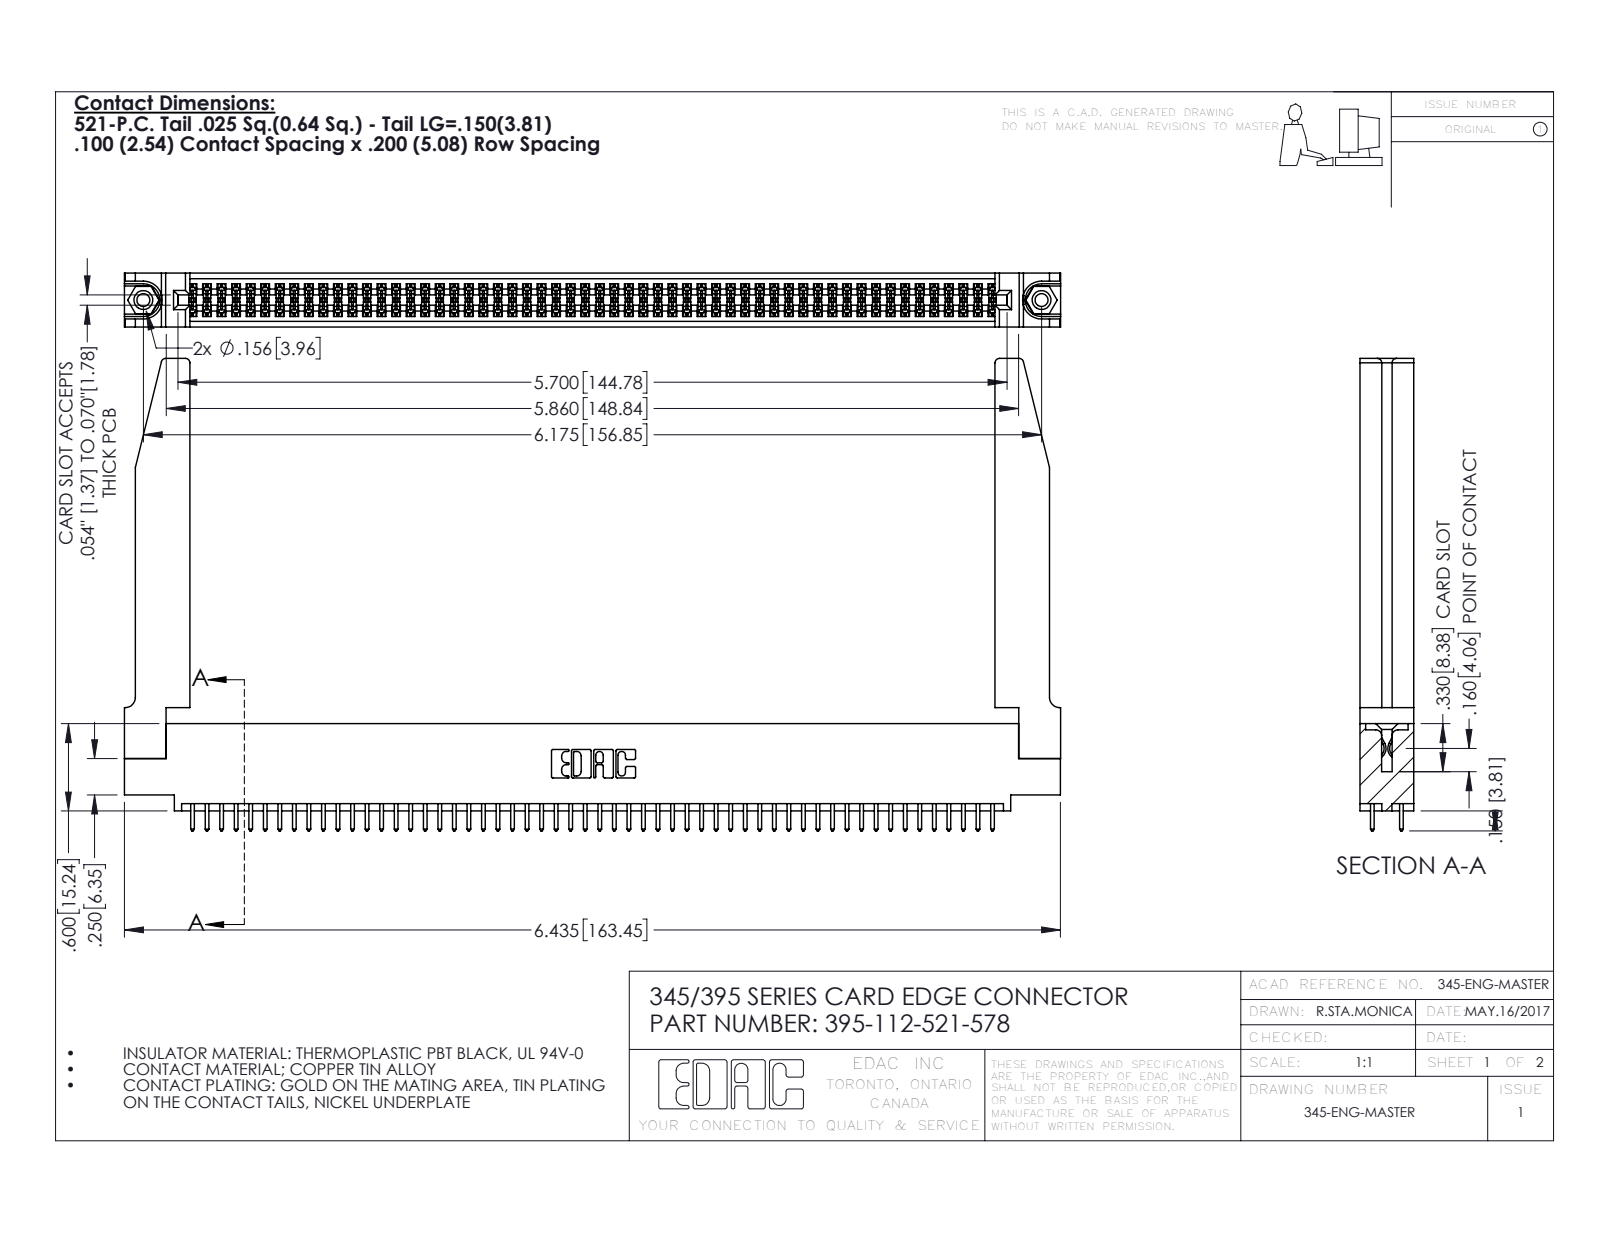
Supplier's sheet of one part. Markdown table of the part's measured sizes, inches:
| quantity | value |
| --- | --- |
| part name | 345-220-078_345-220-078; 345-292-001_345-293-121; 345 Part_0.110 Offset - 0.156 Dia-TH; 345-250-001_345-250-001-102 (+1 more) |
| STEP written by | SolidWorks 2016 (CONFIG_CONTROL_DESIGN) |
| units | inches |
| bodies | 117 solids, 5964 faces (3922 planar, 1990 cylindrical, 52 other) |
| overall size | 6.436 × 3.247 × 0.37 |
| volume | 1.444 in³ |
| surface area | 47.11 in² |
| round holes (diameter × count) | 0.089 × 2, 0.125 × 2, 0.156 × 2, 0.064 × 1 |
| round bosses / shafts (diameter × count) | 0.155 × 2 |
| partial cylindrical surfaces (radius × count) | 0.006 × 168, 0.01 × 112, 0.01 × 22, 0.03 × 8, 0.007 × 6, 0.031 × 6, 0.026 × 3, 0.014 × 2 |
| main face-to-face distances | 0.072, 0.298, 0.37, 0.2, 0.098, 0.272, 0.025, 0.225, 0.175, 0.148 |
| hole center spacings | 0.27, 5.939, 6.175 |
